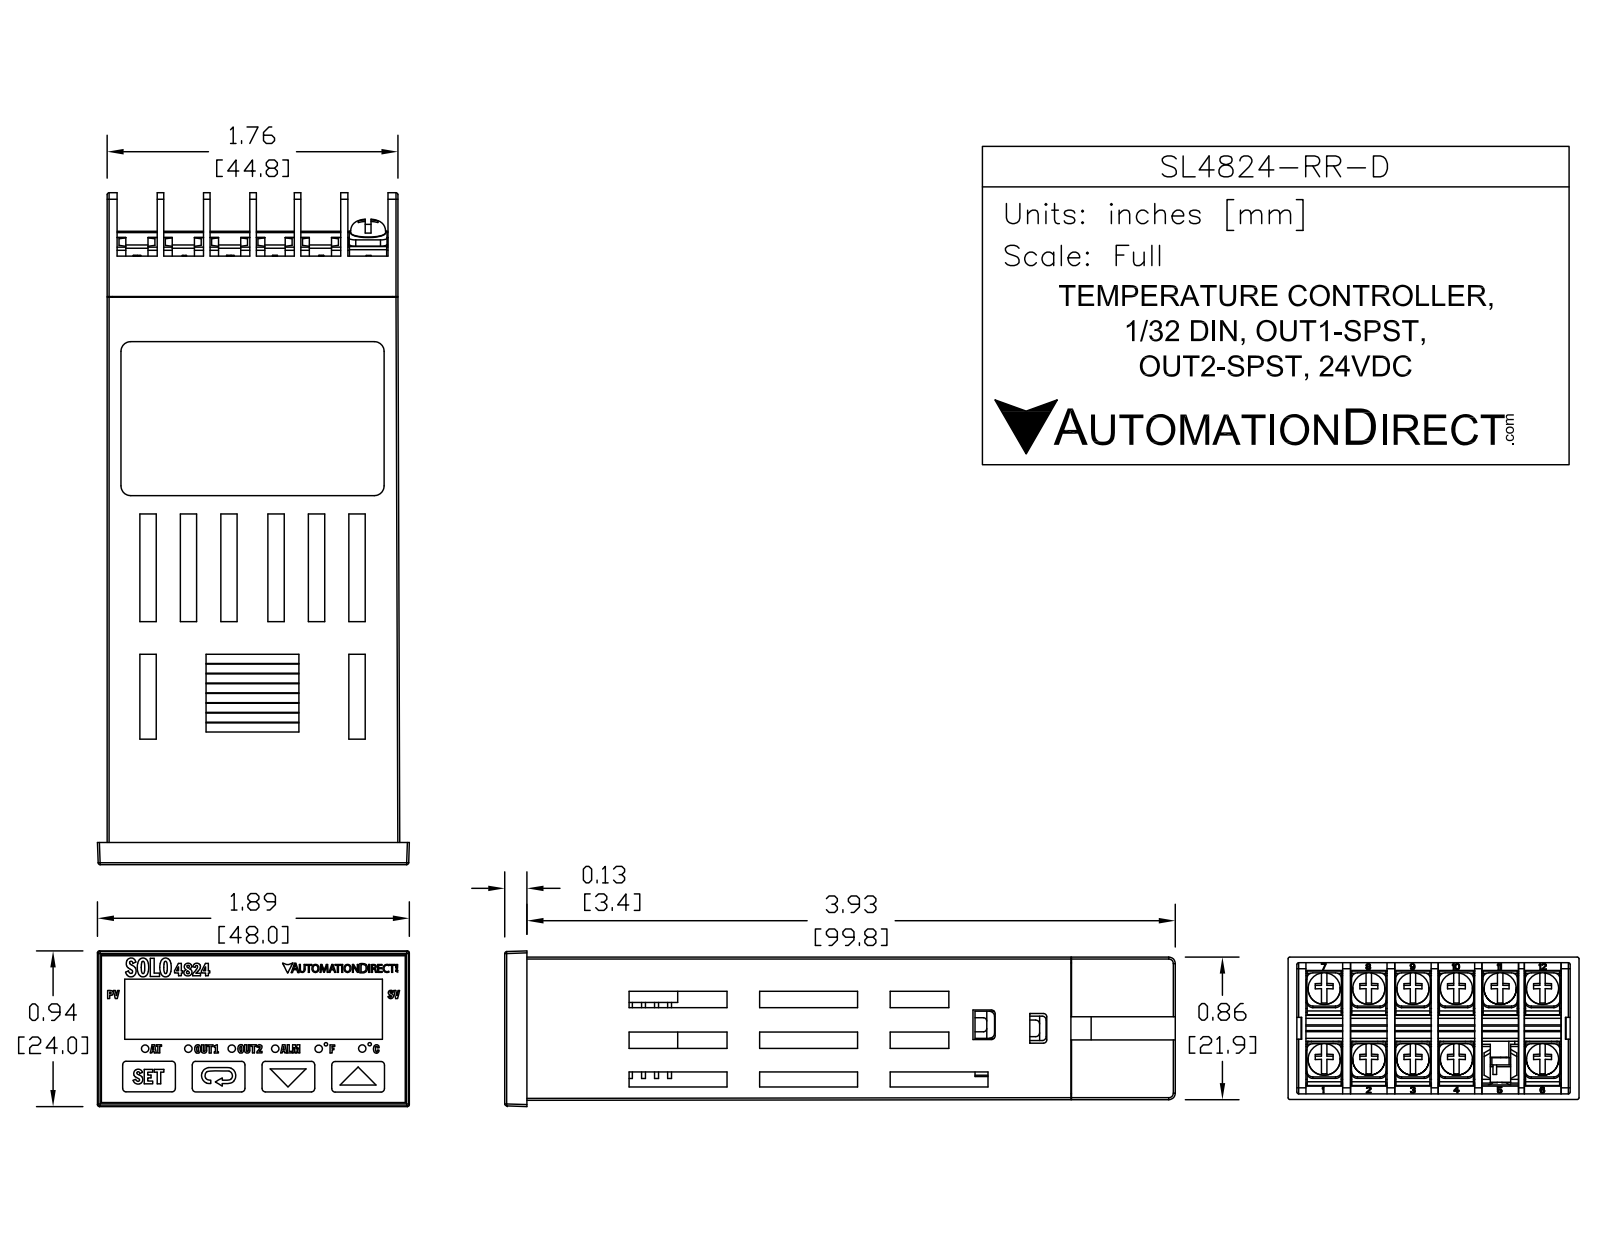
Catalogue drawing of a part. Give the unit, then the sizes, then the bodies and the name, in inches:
Units: inches
Overall size (bounding box): 4.076 × 2.015 × 1.125
Round bosses / shafts (diameter × count): ⌀0.185 ×12
Partial cylindrical surfaces — rounded edges, fillets, slot ends (radius × count): R0.03 ×68, R0.015 ×14, R0.006 ×4, R0.06 ×4, R0.025 ×2, R0.045 ×2
Main face-to-face distances: 0.86, 0.859, 0.06, 1.76, 0.8, 0.28, 1.7, 0.24, 0.858, 0.84
Volume: 5.814 in³ · Surface area: 31.5 in²
Bodies: 1 solid, 992 faces (670 planar, 154 cylindrical, 168 other)
Part name (STEP PRODUCT): SL4824-RR-D
STEP written by: SolidWorks 2011 (AUTOMOTIVE_DESIGN)
